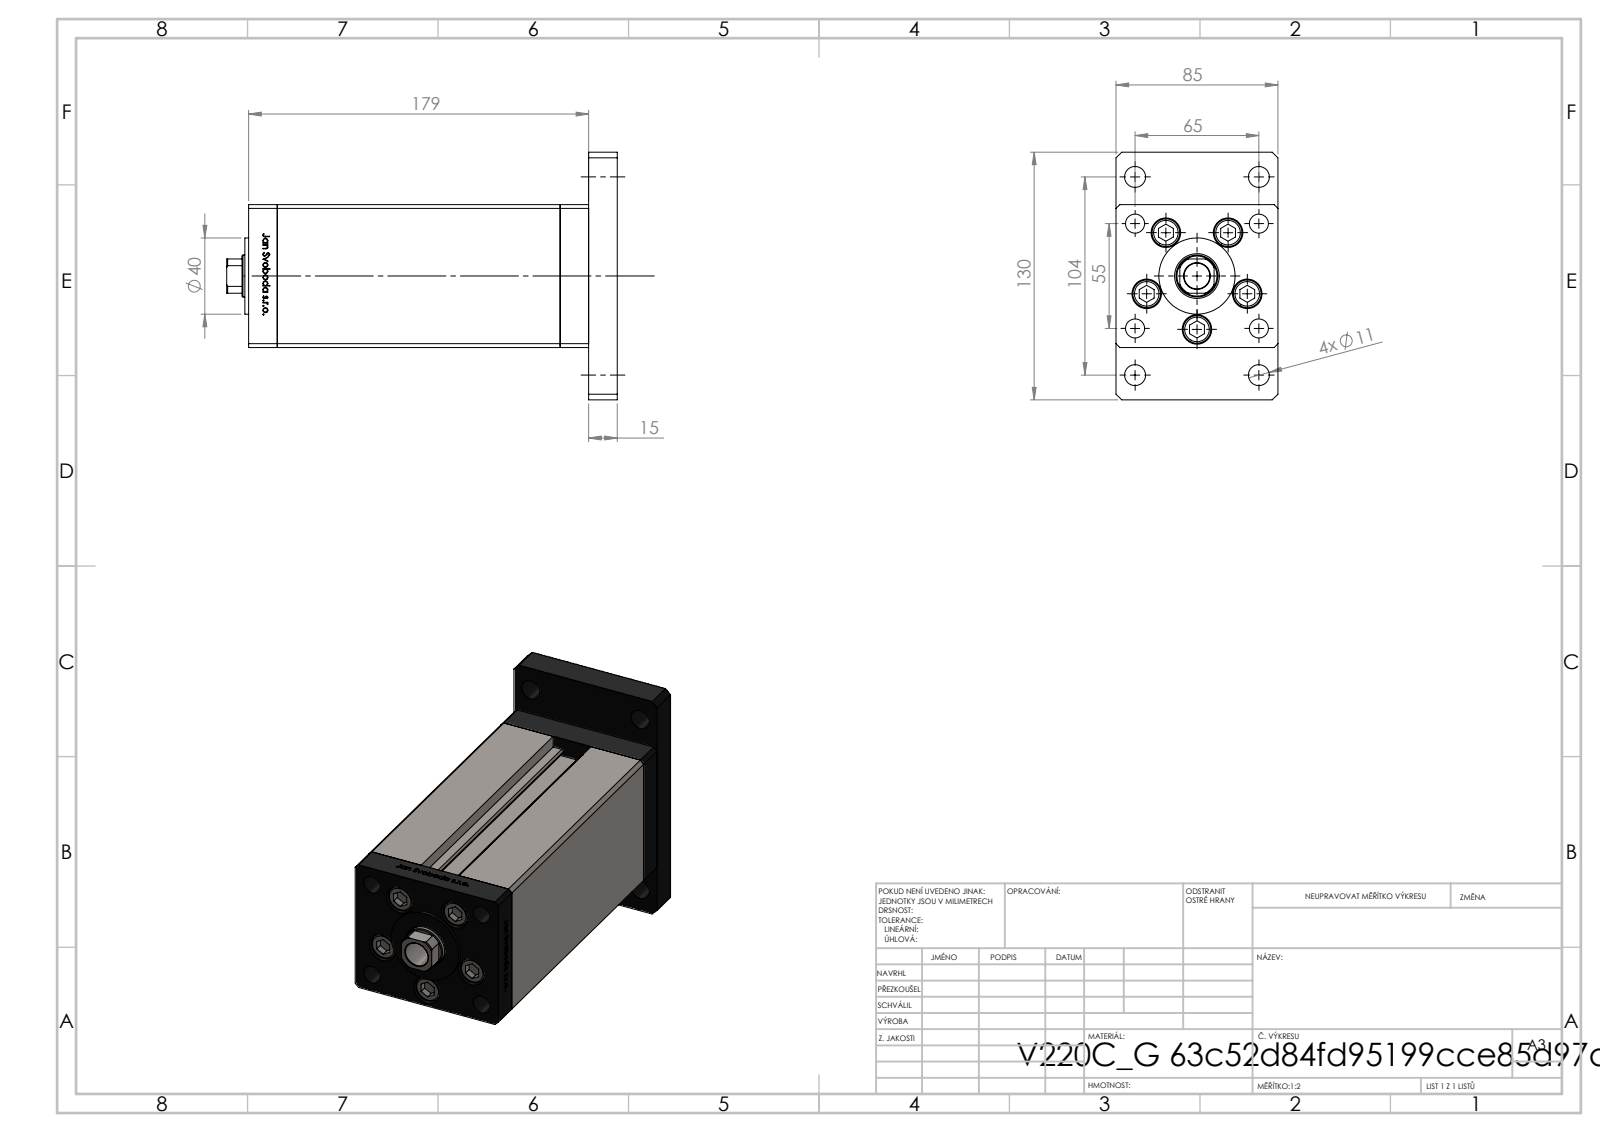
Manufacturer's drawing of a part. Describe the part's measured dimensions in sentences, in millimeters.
The part is named "V220C_G_MIDDLE; V220C_FRONT_G; V220C BACK_G; ALLEN BOLT (+2 more)". Its 3-D file was written by "SolidWorks 2019 (CONFIG_CONTROL_DESIGN)". It is 19 solids with 1301 faces: 514 planar, 181 cylindrical and 606 other. Overall it measures 205 by 130 by 85 millimeters. Its volume is 1 162 000 cubic millimeters and its surface area 196 296 square millimeters. Round holes: 9 of diameter 10, 9 of diameter 11, 5 of diameter 15.5, 4 of diameter 14.5, 1 of diameter 13.5, 1 of diameter 22, 1 of diameter 23.5, 1 of diameter 56. Round bosses or shafts: 9 of diameter 8, 5 of diameter 14.5, 1 of diameter 40. Partial cylindrical surfaces (rounded edges, fillets, slot ends): 2 of radius 0.93, 1 of radius 10.5. The main face-to-face distances are 15, 85, 163.5, 178.5, 75, 148.5, 30, 2, 176.5, 193.5. The hole center spacings are 28, 24.5, 42.57, 61.32, 65, 69.46, 79.5, 102.69.
